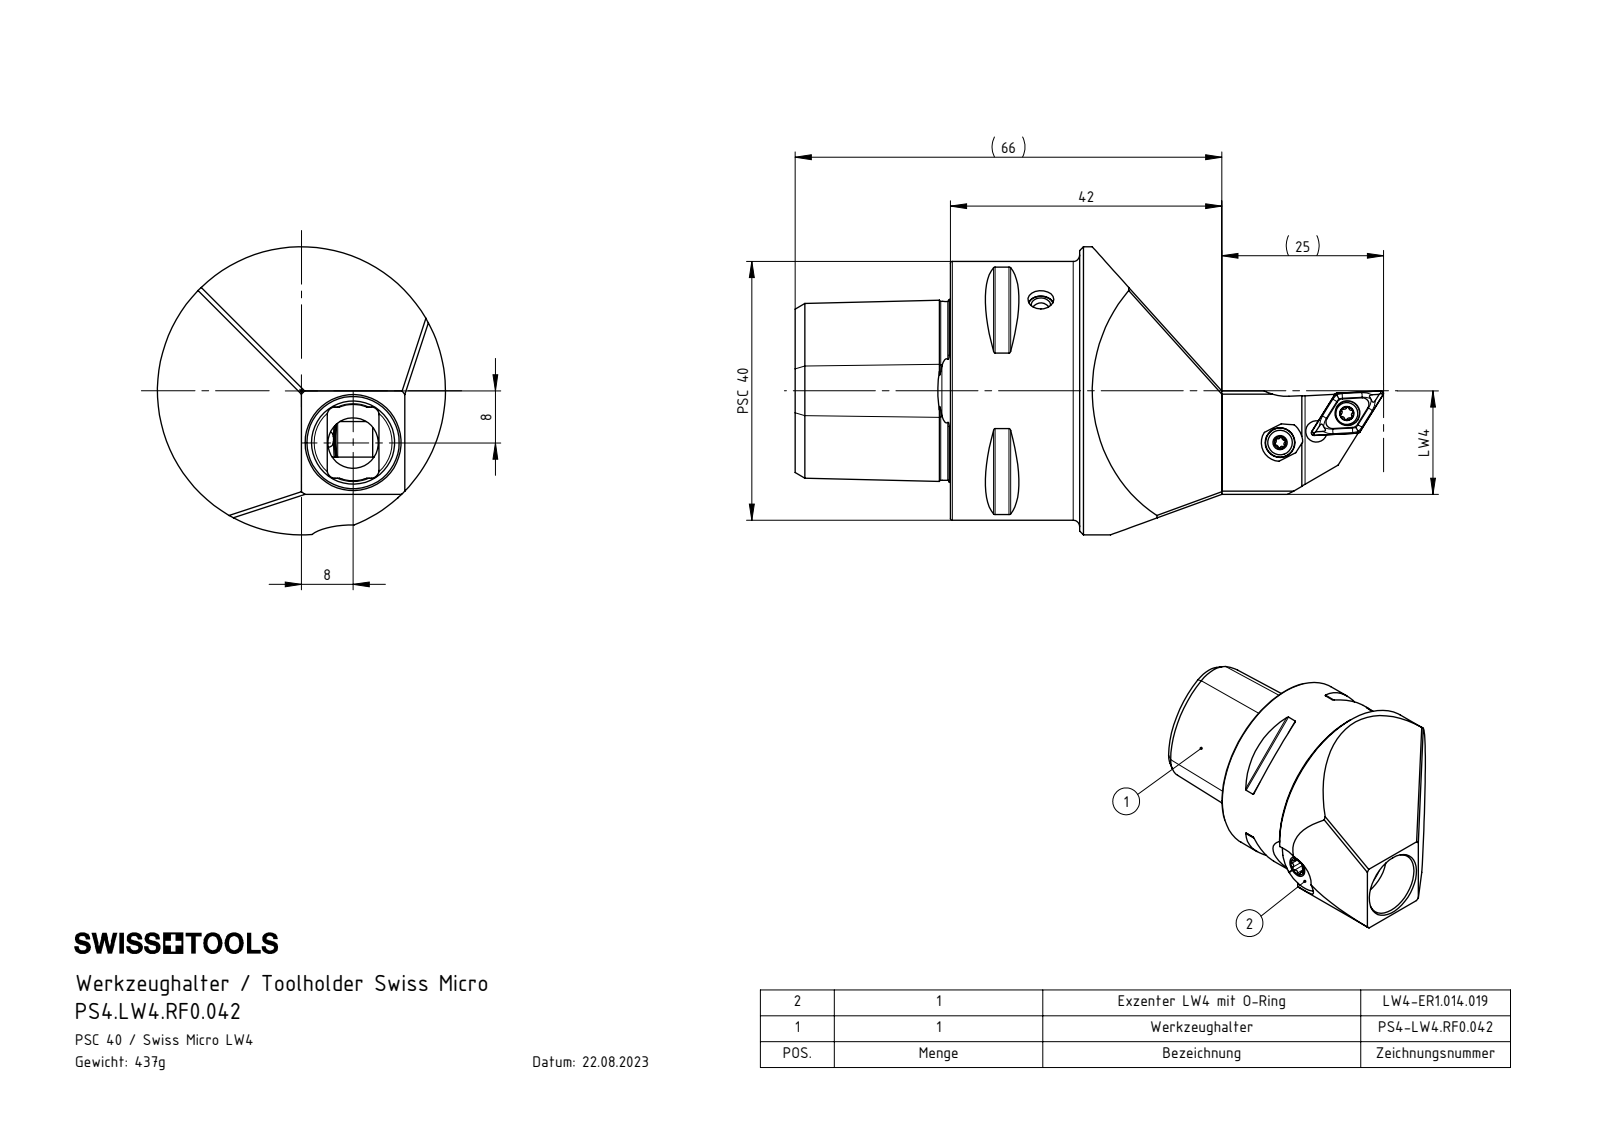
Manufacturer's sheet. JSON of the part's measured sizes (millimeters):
{"part_name": "DIN 3771 - 10x1; PS4-LW4.RF0.042_A; LW4-ER1.014.019_D_Standard<Wie bearbeitet>; LW4-ER1.014.019 (+2 more)", "step_written_by": "SolidWorks 2017 (AUTOMOTIVE_DESIGN)", "units": "millimeters", "bodies": {"solids": 6, "faces": 335, "planar": 69, "cylindrical": 103, "other": 163}, "overall_size": [66, 44.55, 44.55], "volume_mm3": 49942, "surface_area_mm2": 14147, "round_holes": [[3.3, 2], [4, 2], [1, 1], [2.85, 1], [3, 1], [4.6, 1], [7.8, 1], [12.5, 1], [12.86, 1], [14, 1], [18, 1], [20, 1]], "round_bosses_or_shafts": [[44.55, 1], [40, 1], [12, 1], [10.2, 1], [4, 1]], "partial_cylinders_radius": [[0.3, 8], [0.4, 6], [0.69, 6], [1.2, 4], [2.75, 2], [3, 1], [4.1, 1], [4.15, 1]], "face_to_face_distances": [24, 15.52, 29, 66, 42, 44, 20, 22, 35.3, 8.8], "hole_center_spacings": [11.31, 11.36, 23.5]}
